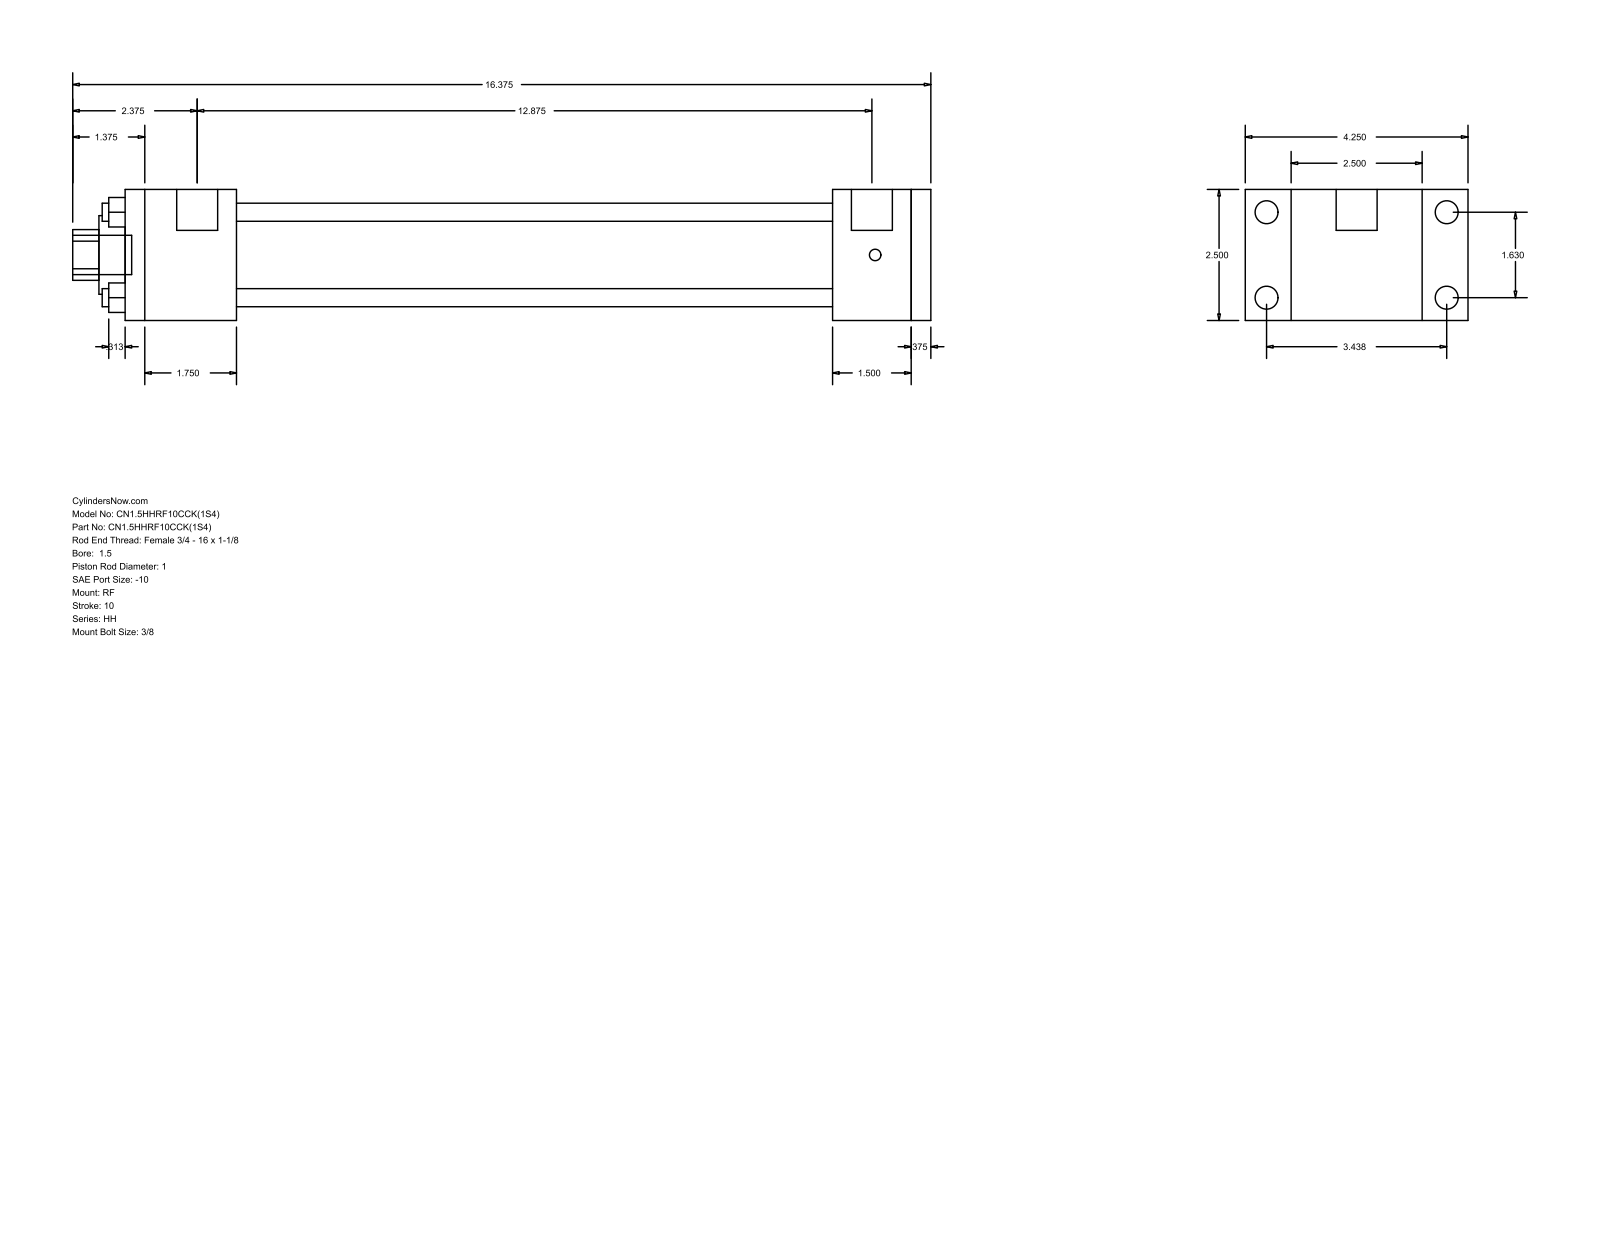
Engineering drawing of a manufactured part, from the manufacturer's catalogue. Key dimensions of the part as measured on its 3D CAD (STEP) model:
Part name (STEP PRODUCT): HH_RF__0150_1
STEP written by: GSSL Pune (CONFIG_CONTROL_DESIGN)
Units: millimetres
Bodies: 0 solids, 92 faces (64 planar, 28 cylindrical, 0 other)
Overall size (bounding box): 415.93 × 107.95 × 63.5
Round holes (diameter × count): ⌀8.76 ×4, ⌀25.4 ×1, ⌀38.1 ×1, ⌀44.45 ×1
Round bosses / shafts (diameter × count): ⌀11.13 ×4, ⌀5.56 ×4, ⌀19.84 ×2, ⌀19.05 ×1
Partial cylindrical surfaces — rounded edges, fillets, slot ends (radius × count): R12.29 ×1
Main face-to-face distances: 63.5, 9.53, 288.92, 327.02, 336.55, 38.1, 47.63, 53.98, 342.9, 381
Hole centre spacings: 29.27, 41.4, 58.55
